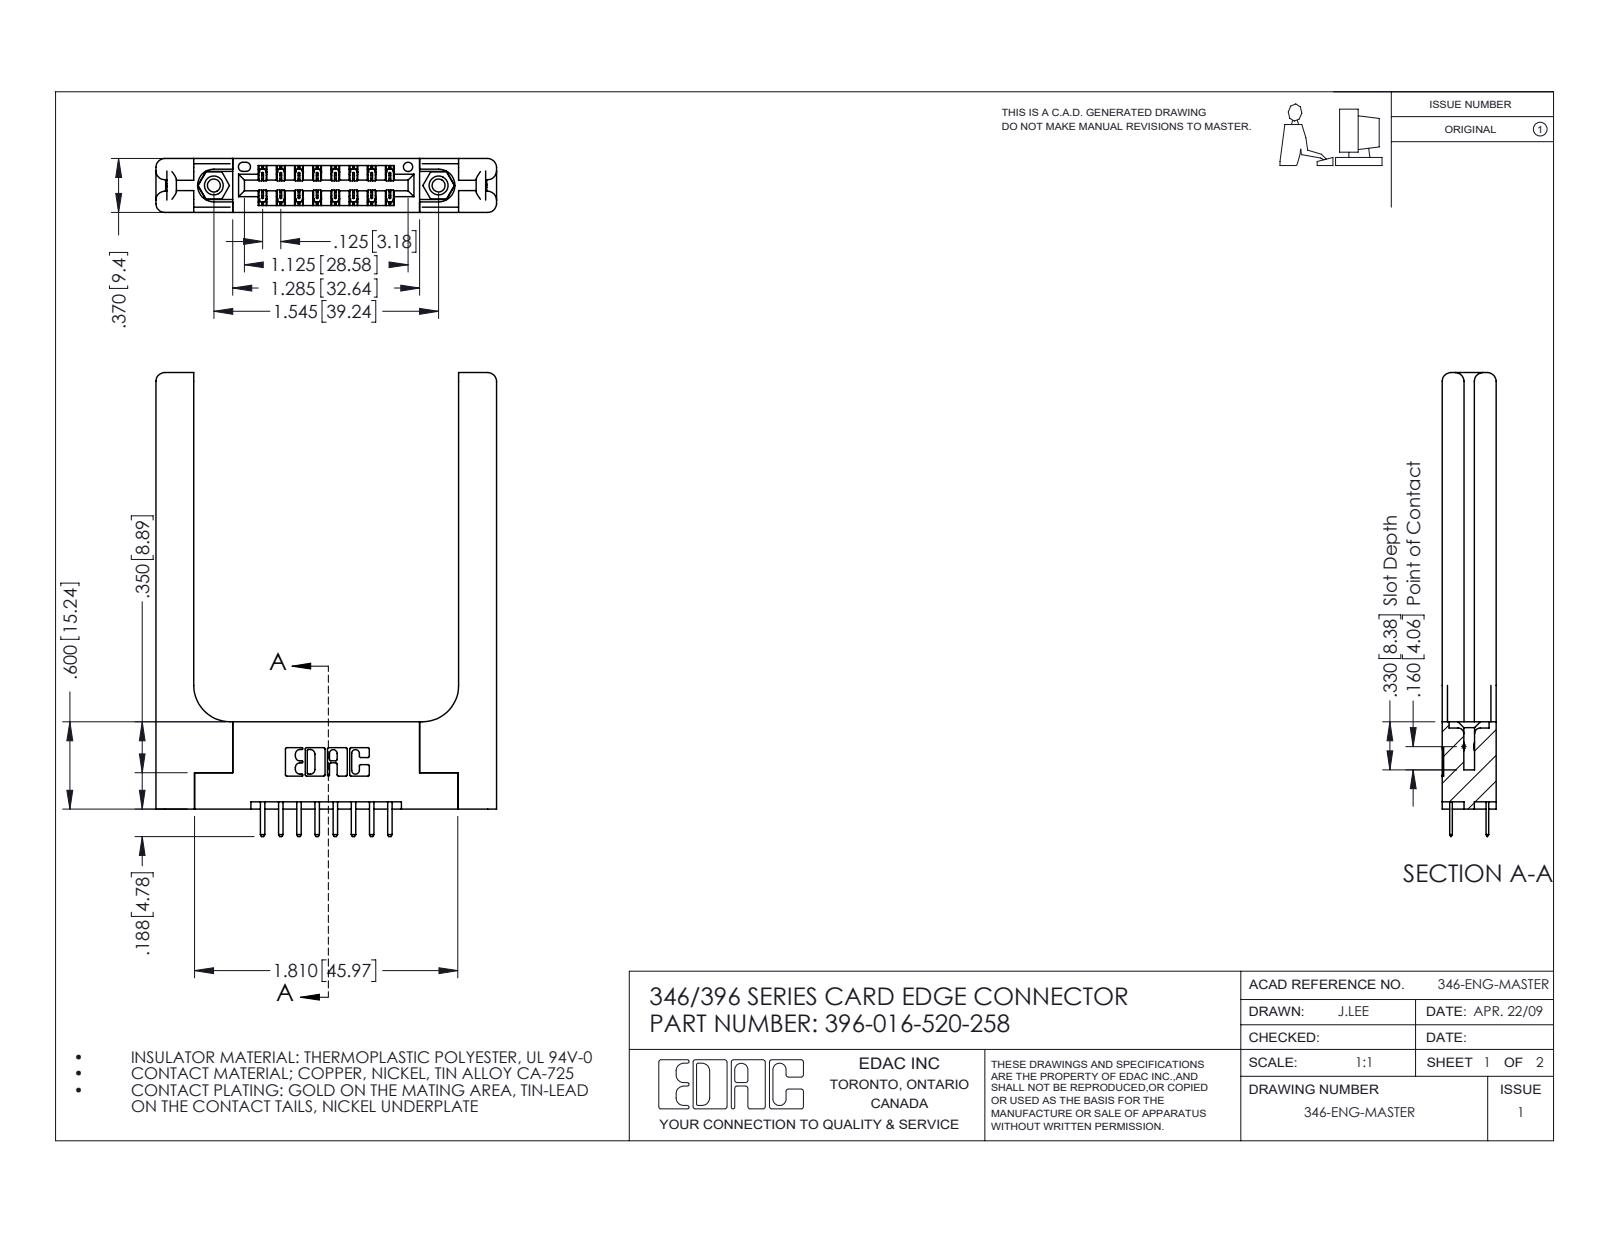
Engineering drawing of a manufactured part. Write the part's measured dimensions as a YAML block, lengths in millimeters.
part_name: "345-250-001_345-250-001-102; 346 Part_Flush Mounting Lugs - 0.156 Dia-TH; 345-292-001_345-293-120; 396-016-520-258 (+1 more)"
step_written_by: "SolidWorks 2016 (CONFIG_CONTROL_DESIGN)"
units: millimeters
bodies: {solids: 21, faces: 1274, planar: 816, cylindrical: 398, other: 60}
overall_size: [81, 59.5, 9.4]
volume: 13000
surface_area: 12020
round_holes:
  - {diameter: 2.3, count: 2}
  - {diameter: 3.2, count: 2}
  - {diameter: 4, count: 2}
  - {diameter: 1.6, count: 1}
round_bosses_or_shafts:
  - {diameter: 3.9, count: 2}
partial_cylinders:
  - {radius: 0.2, count: 24}
  - {radius: 0.3, count: 22}
  - {radius: 0.3, count: 20}
  - {radius: 1.5, count: 16}
  - {radius: 0.2, count: 6}
  - {radius: 0.8, count: 6}
  - {radius: 0.7, count: 3}
  - {radius: 0.4, count: 2}
face_to_face_distances: [9.4, 3.8, 5.6, 6.4, 1.8, 3.8, 2.6, 1.2, 8.2, 4.4]
hole_center_spacings: [6.2, 34.1, 39.2]
